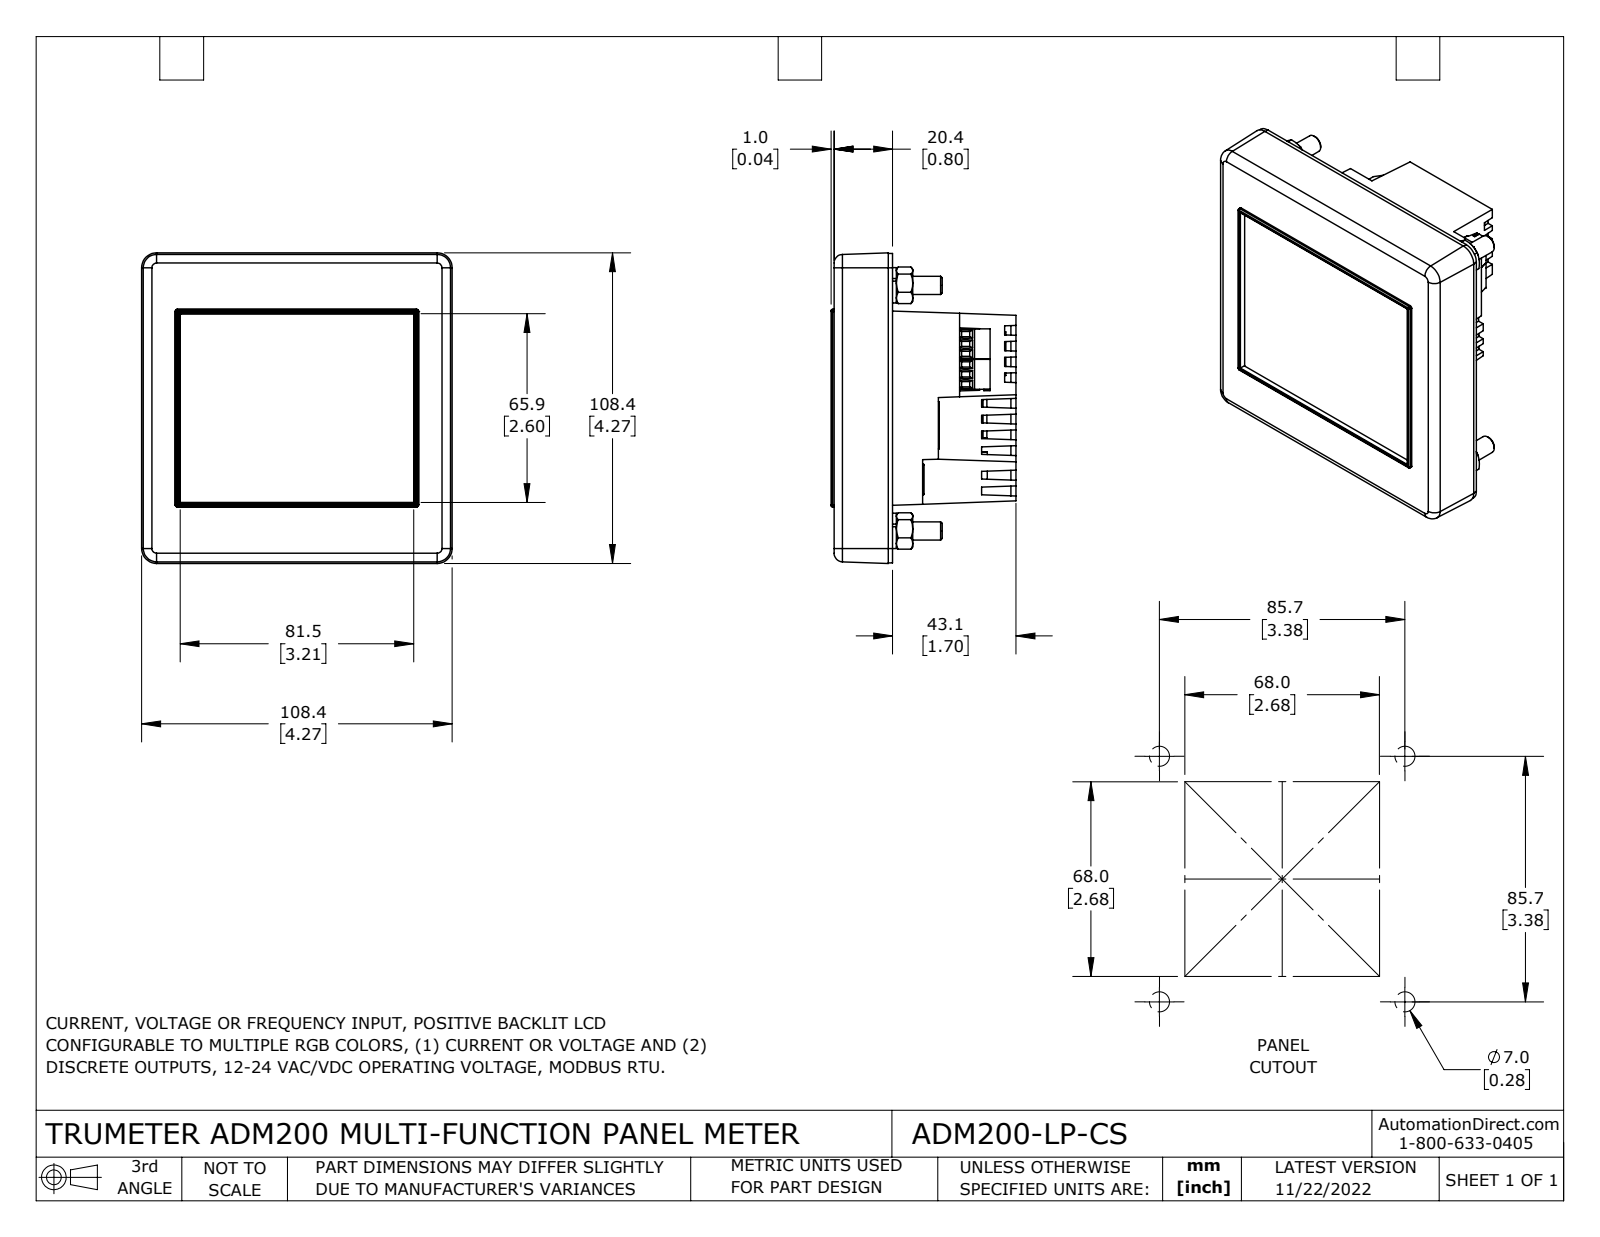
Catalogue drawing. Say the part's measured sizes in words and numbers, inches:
The part is named "ADM200-LP-CS". Its 3-D file was written by "SolidWorks 2021 (CONFIG_CONTROL_DESIGN)". It is 23 solids with 2059 faces: 1384 planar, 290 cylindrical and 385 other. Overall it measures 4.269 by 4.269 by 2.541 inches. Its volume is 7.808 cubic inches and its surface area 190.8 square inches. Round holes: 9 of diameter 0.071, 6 of diameter 0.114, 5 of diameter 0.118, 4 of diameter 0.213, 4 of diameter 0.25, 4 of diameter 0.26, 4 of diameter 0.295, 2 of diameter 0.154. Round bosses or shafts: 5 of diameter 0.039, 4 of diameter 0.487, 4 of diameter 0.438, 4 of diameter 0.024, 2 of diameter 0.079. Partial cylindrical surfaces (rounded edges, fillets, slot ends): 32 of radius 0.006, 30 of radius 0.02, 7 of radius 0.039, 4 of radius 0.016, 4 of radius 0.03, 4 of radius 0.118, 4 of radius 0.197, 2 of radius 0.004. The main face-to-face distances are 0.031, 0.635, 0.11, 0.073, 0.059, 0.079, 0.694, 3.395, 3.468, 0.047. The hole center spacings are 0.709, 3.228, 0.136, 0.293, 0.986, 1.417, 2.126, 2.399.
